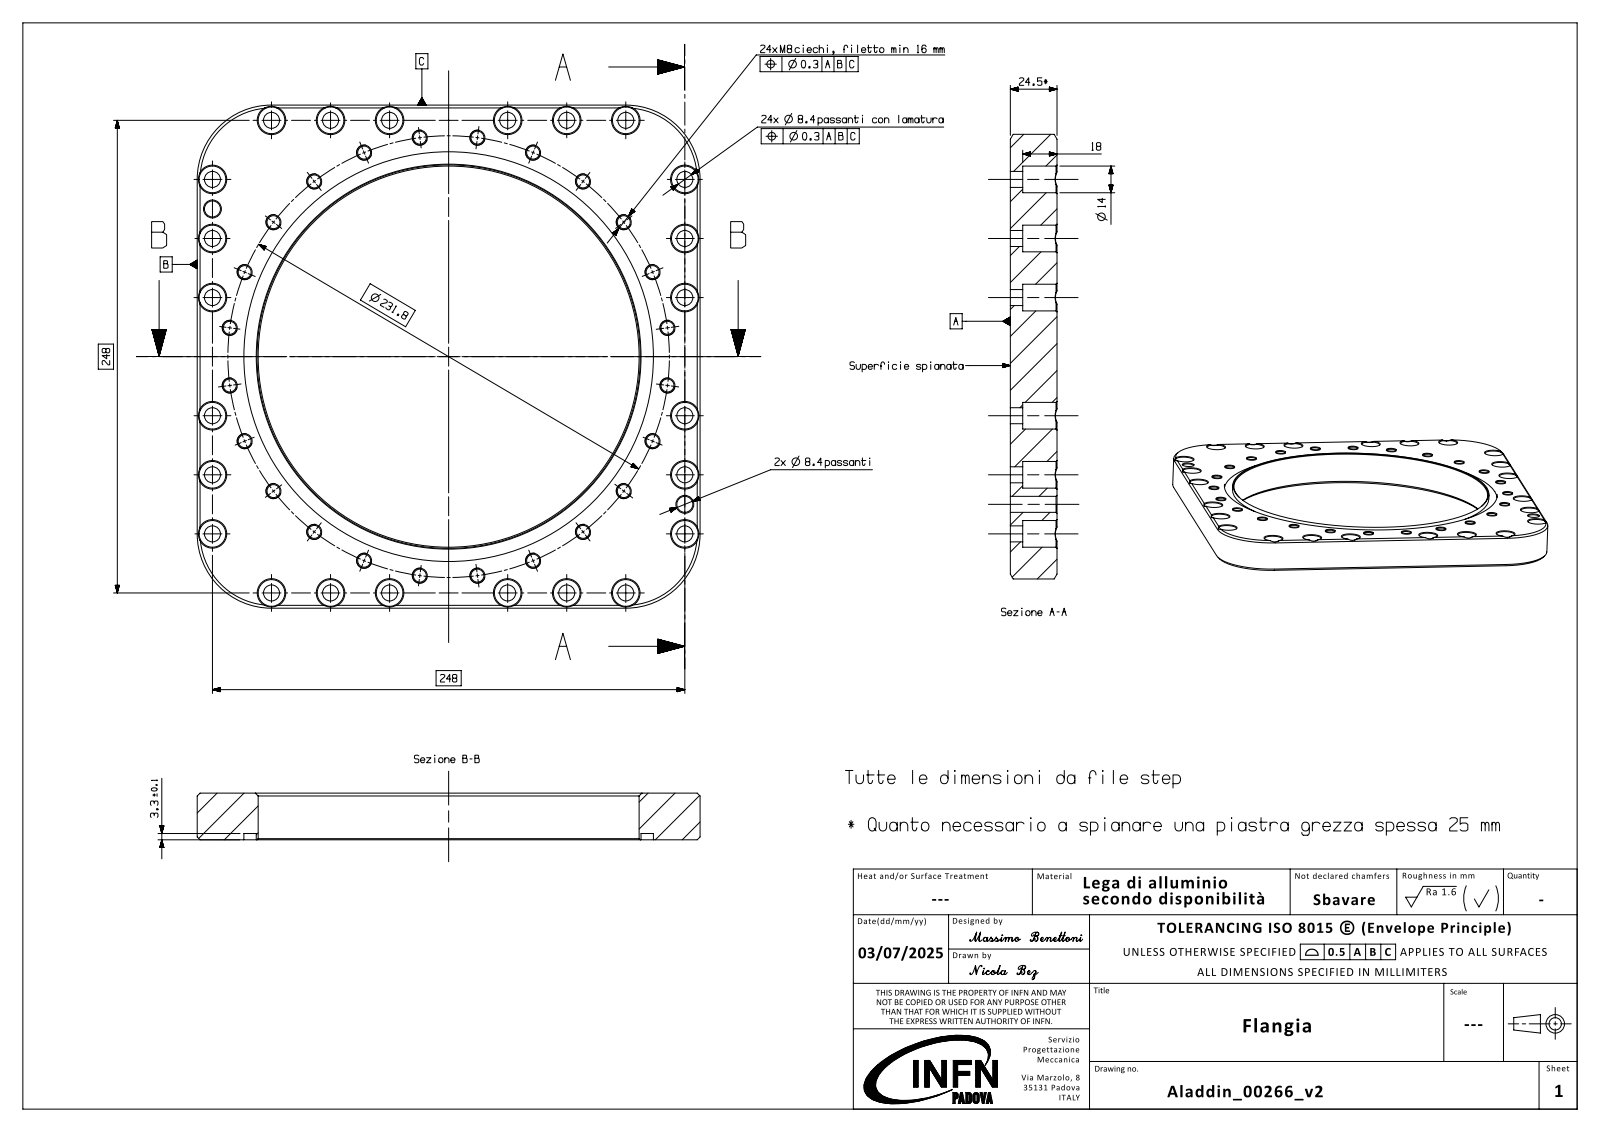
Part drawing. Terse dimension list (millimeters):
name: IR3_00000266_flangia_v2_objects
written by: SIEMENS PLM Software NX2306.5001 (AUTOMOTIVE_DESIGN)
unit: mm
bodies: 1 solid, 239 faces (64 planar, 81 cylindrical, 94 other)
size: 264 × 264 × 24.5
volume: 794 575 mm³; area: 145 714 mm²
holes: 26× ⌀8.4, 24× ⌀6.8, 24× ⌀14, 1× ⌀200, 1× ⌀215
bosses: 1× ⌀202
rounds: 4× R39
face distances: 24.5, 264, 21.2, 3.3, 6.5, 14.7, 18, 6, 0.5, 15.2
hole spacings: 31, 249.93, 155, 62, 124, 248, 255.63, 277.27
